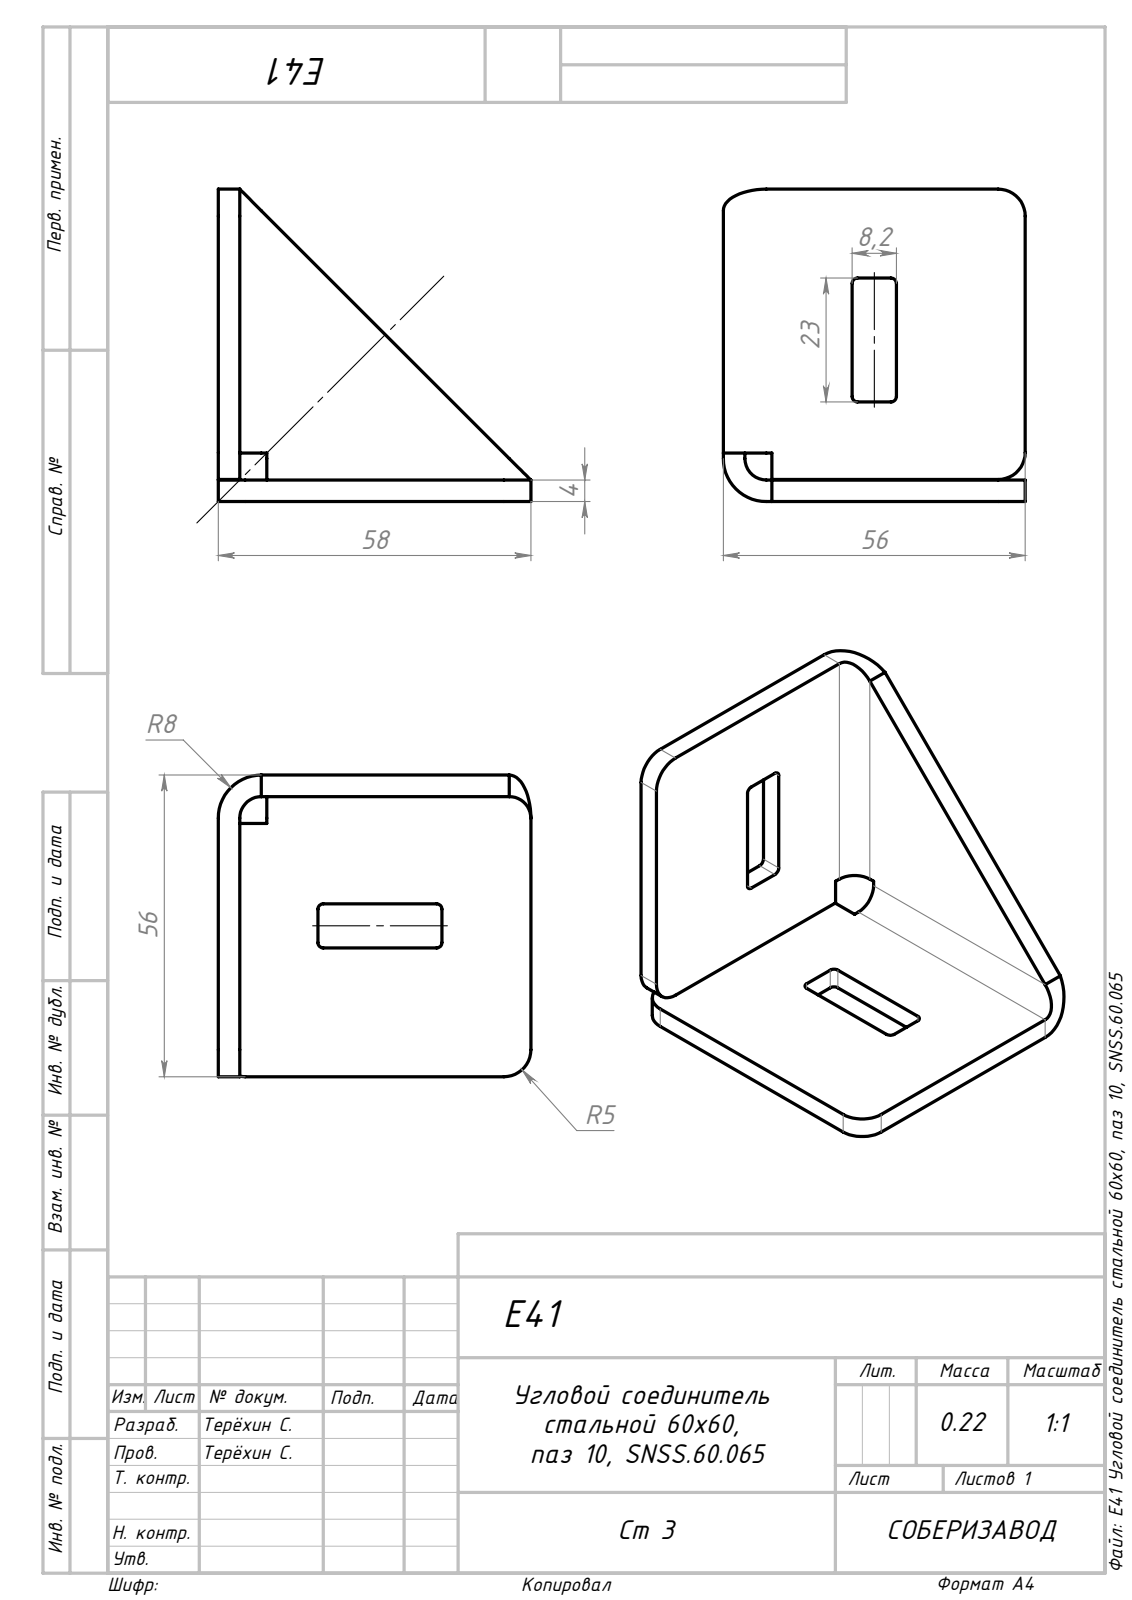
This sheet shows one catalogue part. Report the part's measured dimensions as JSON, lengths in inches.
{"part_name": "E41 Угловой соединитель стальной 60х60, паз 10, SNSS.60.065_00; Сборка1", "step_written_by": "SolidWorks 2022 (AUTOMOTIVE_DESIGN)", "units": "inches", "bodies": {"solids": 1, "faces": 47, "planar": 29, "cylindrical": 16, "other": 2}, "overall_size": [2.283, 2.283, 2.205], "volume_in3": 1.688, "surface_area_in2": 24.76, "partial_cylinders_radius": [[0.039, 8], [0.197, 4], [0.157, 2], [0.315, 2]], "face_to_face_distances": [0.157, 2.205, 2.047, 2.283, 2.126, 0.941, 1.264, 0.161, 2.122, 0.783]}
